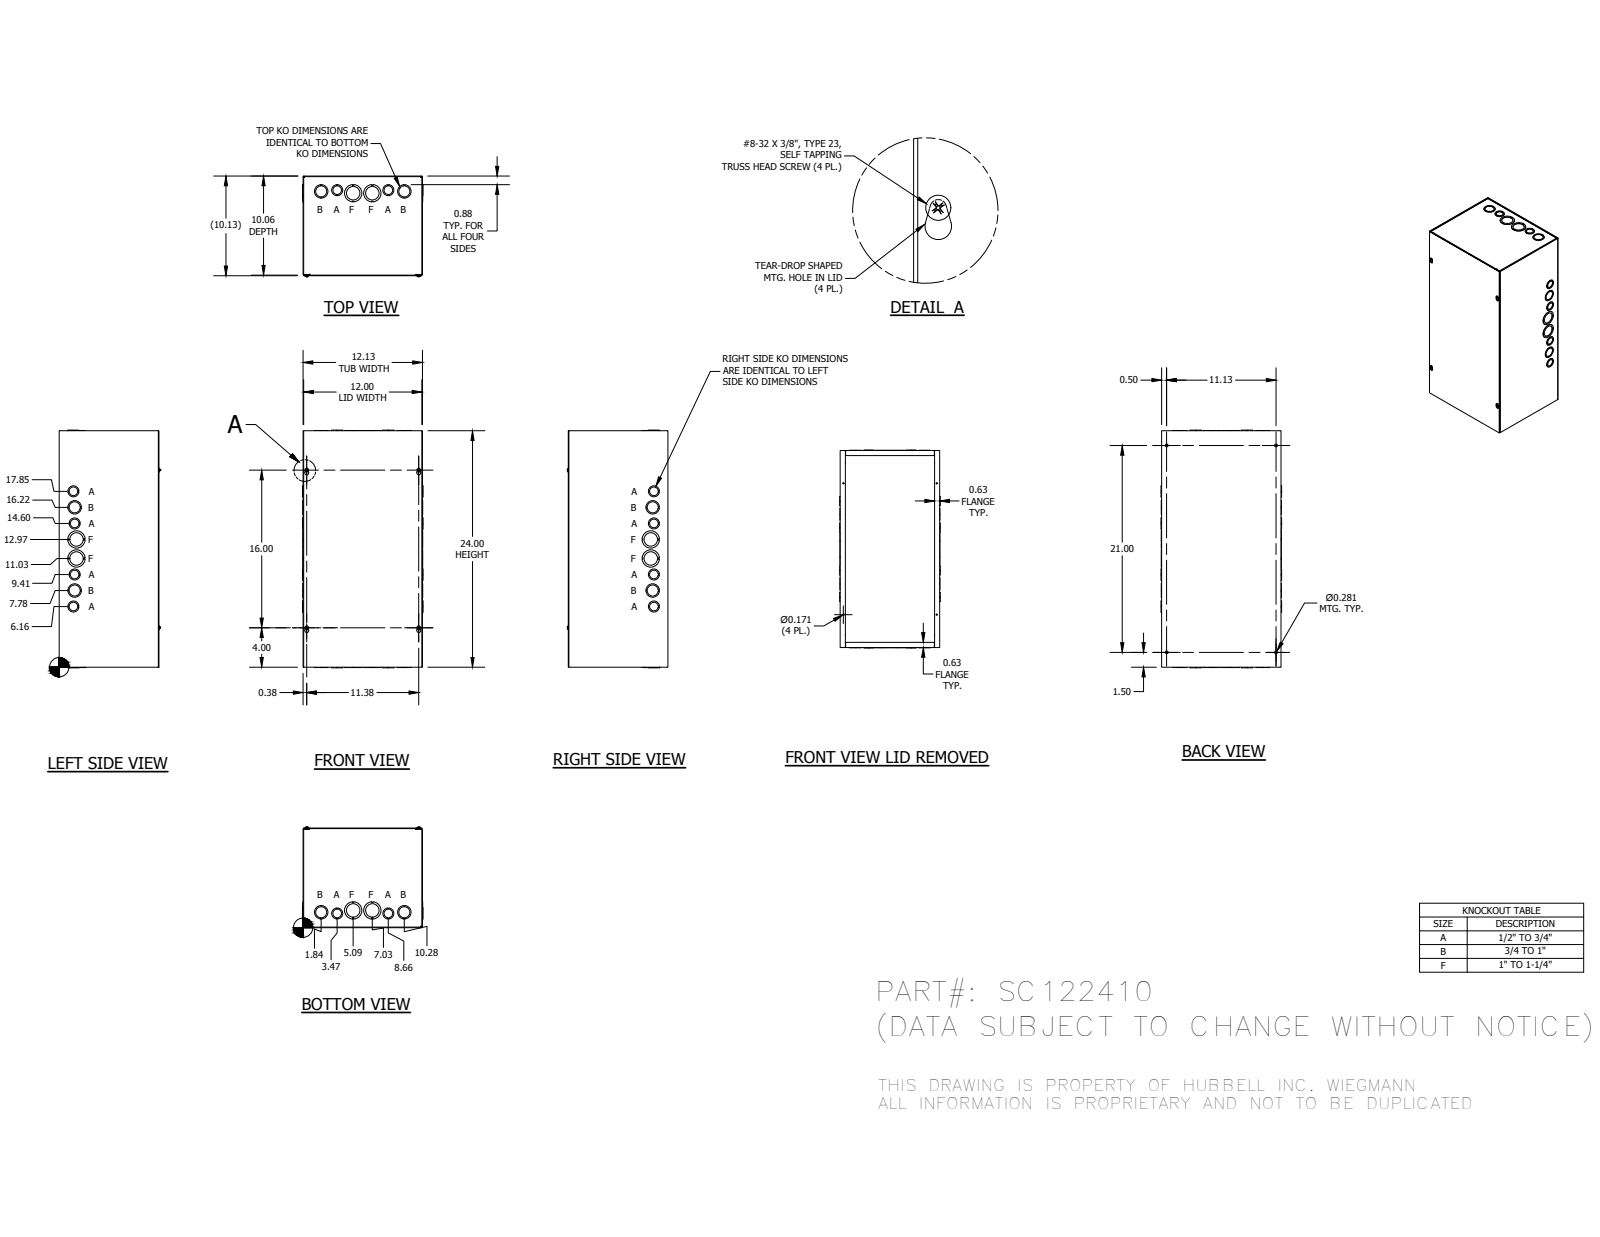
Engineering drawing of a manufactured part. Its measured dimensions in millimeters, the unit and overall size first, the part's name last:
Units: millimetres
Overall size (bounding box): 612.77 × 311.15 × 259.72
Round holes (diameter × count): ⌀28.57 ×12, ⌀22.22 ×8, ⌀34.92 ×8, ⌀4.34 ×4, ⌀7.14 ×4, ⌀44.45 ×4
Round bosses / shafts (diameter × count): ⌀9.75 ×4, ⌀4.17 ×4
Partial cylindrical surfaces — rounded edges, fillets, slot ends (radius × count): R0.79 ×12, R2.38 ×12, R3.17 ×4, R5.16 ×4
Main face-to-face distances: 1.59, 255.59, 306.39, 254, 257.18, 304.8, 307.98, 608.01, 609.6, 606.42
Hole centre spacings: 41.4, 42.03, 63.58, 82.69, 90.9, 131.92, 173.13, 292.72
Bodies: 29 solids, 1055 faces (771 planar, 216 cylindrical, 68 other)
Part name (STEP PRODUCT): SC122410BLR; SC1210TB; SC1224LPA; 34056 (+1 more)
STEP written by: Autodesk Inventor 2014 (AUTOMOTIVE_DESIGN)
